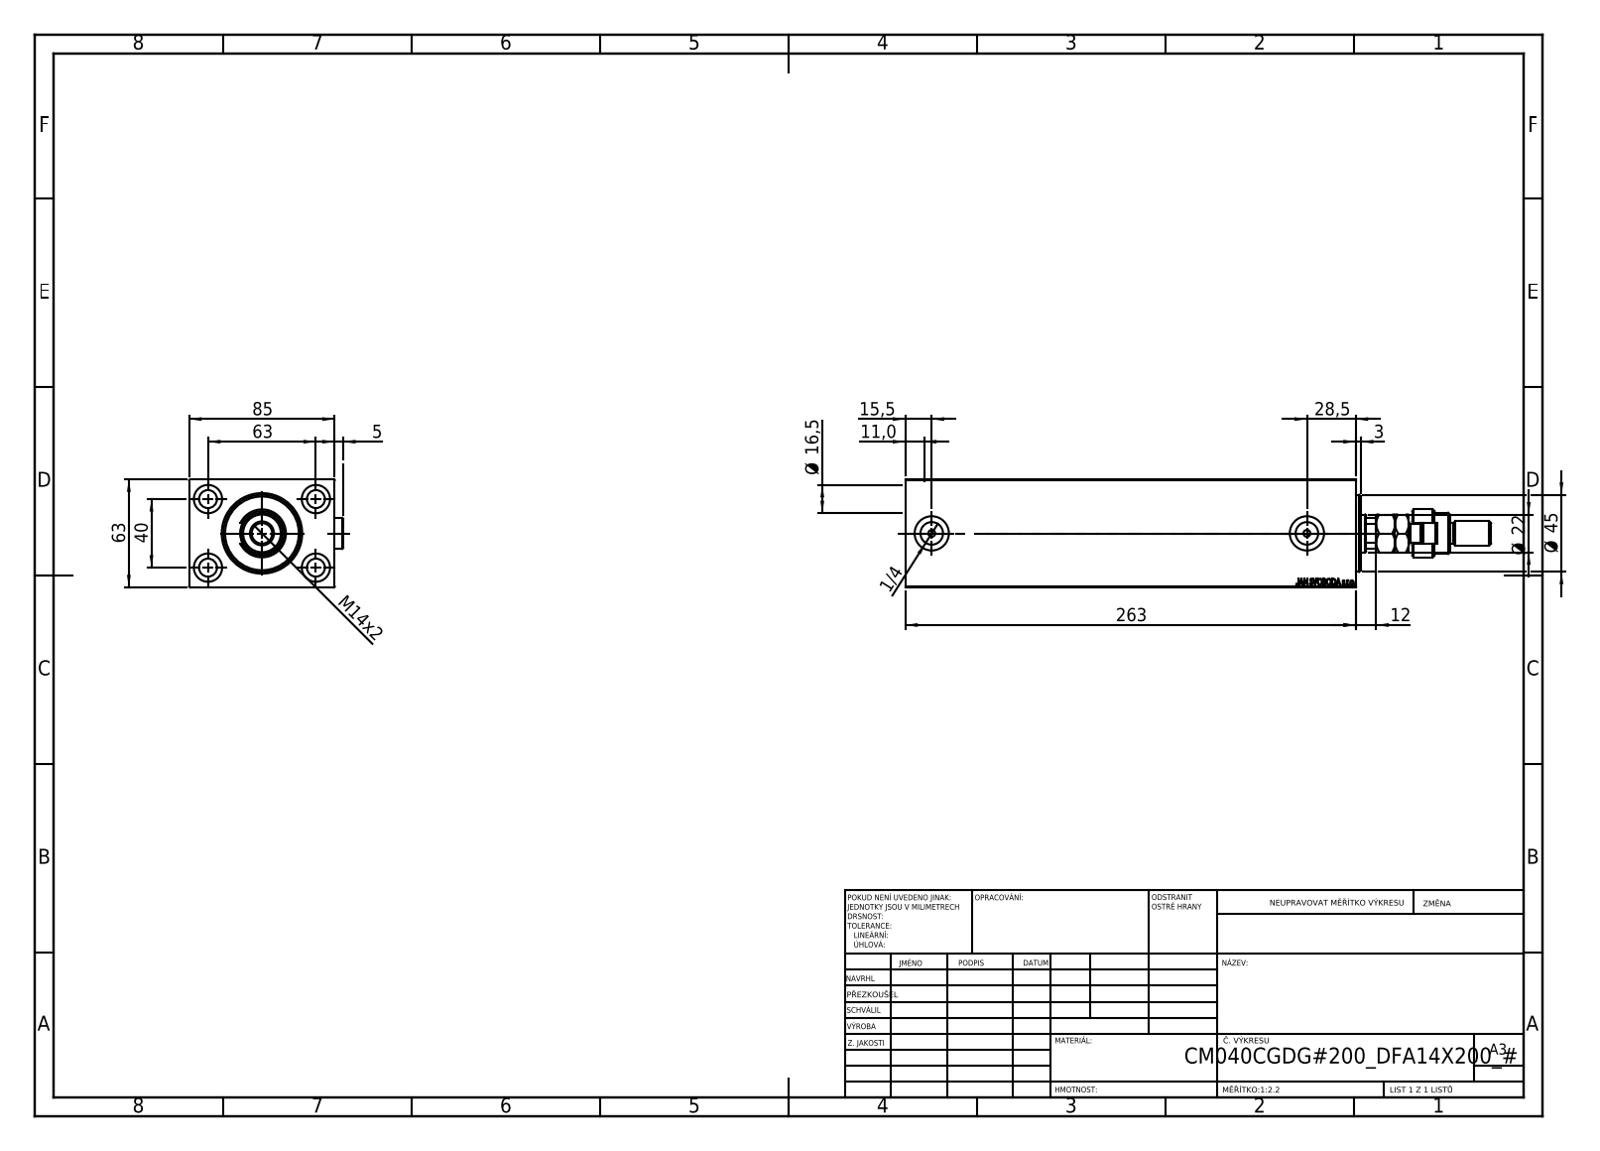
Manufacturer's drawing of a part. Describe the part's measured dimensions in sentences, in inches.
The part is named "FEMALE_PART_FOR_DFA; V450CM_VC_B; V450CM_C_Body; MFA (+2 more)". Its 3-D file was written by "SolidWorks 2019 (CONFIG_CONTROL_DESIGN)". It is 7 solids with 1001 faces: 470 planar, 89 cylindrical and 442 other. Overall it measures 13.465 by 3.539 by 2.48 inches. Its volume is 70.3 cubic inches and its surface area 305.2 square inches. Round holes: 4 of diameter 0.413, 4 of diameter 0.65, 2 of diameter 0.157, 2 of diameter 0.518, 2 of diameter 0.787, 1 of diameter 0.492, 1 of diameter 0.866, 1 of diameter 1.004, 1 of diameter 1.575, 1 of diameter 1.654, 1 of diameter 1.772. Round bosses or shafts: 3 of diameter 0.709, 1 of diameter 1.102, 1 of diameter 0.945, 1 of diameter 0.551, 1 of diameter 0.472, 1 of diameter 0.433. Partial cylindrical surfaces (rounded edges, fillets, slot ends): 1 of radius 0.384, 1 of radius 0.413. The main face-to-face distances are 2.48, 3.346, 0.472, 9.882, 10.354, 3.343, 0.118, 0.591, 9.409, 2.008. The hole center spacings are 1.469, 1.575, 2.48, 2.938, 8.622.
